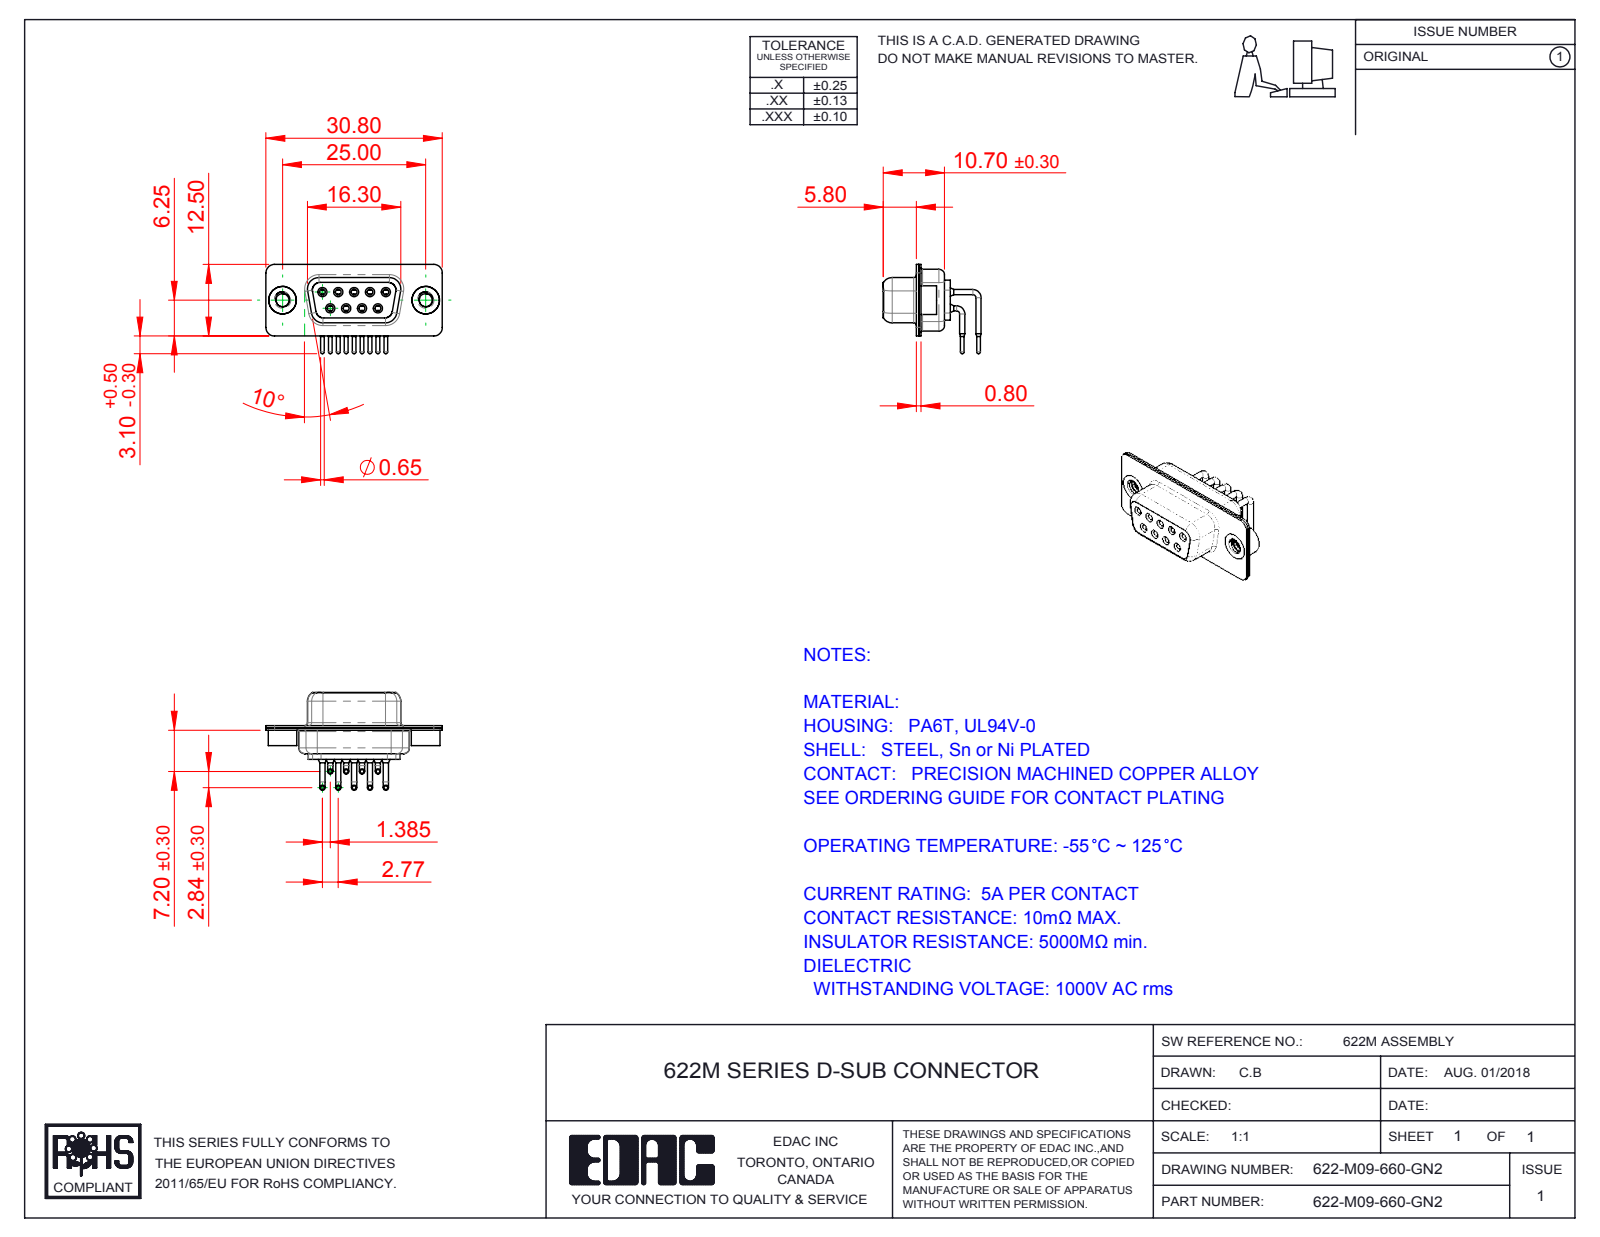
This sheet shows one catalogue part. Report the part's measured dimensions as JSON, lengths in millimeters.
{"part_name": "622M Contact Row 2; 622M Shell Front_09 Contacts; 622M Contact Row 1; 622M Shell Rear_09 Contacts (+3 more)", "step_written_by": "SolidWorks 2016 (CONFIG_CONTROL_DESIGN)", "units": "millimeters", "bodies": {"solids": 14, "faces": 756, "planar": 202, "cylindrical": 344, "other": 210}, "overall_size": [30.8, 17.09, 15.6], "volume_mm3": 1745, "surface_area_mm2": 4559, "round_holes": [[1, 9], [1.1, 9], [1.7, 9], [1.8, 9], [2, 9], [2.26, 2], [4, 2], [4.8, 2]], "round_bosses_or_shafts": [[0.9, 18], [1.6, 9], [1.5, 9], [0.65, 9], [5, 2], [4.9, 2]], "partial_cylinders_radius": [[1.5, 16], [2, 12], [1.35, 8], [1.6, 8], [0.25, 4], [0.5, 4], [0.6, 4], [0.65, 4]], "face_to_face_distances": [0.4, 0.8, 1.45, 2.3, 8.95, 6.2, 8.5, 1.9, 0.85, 9.35], "hole_center_spacings": [3.16, 2.77, 5.54, 5.03, 5.04, 8.31, 7.1, 7.48]}
